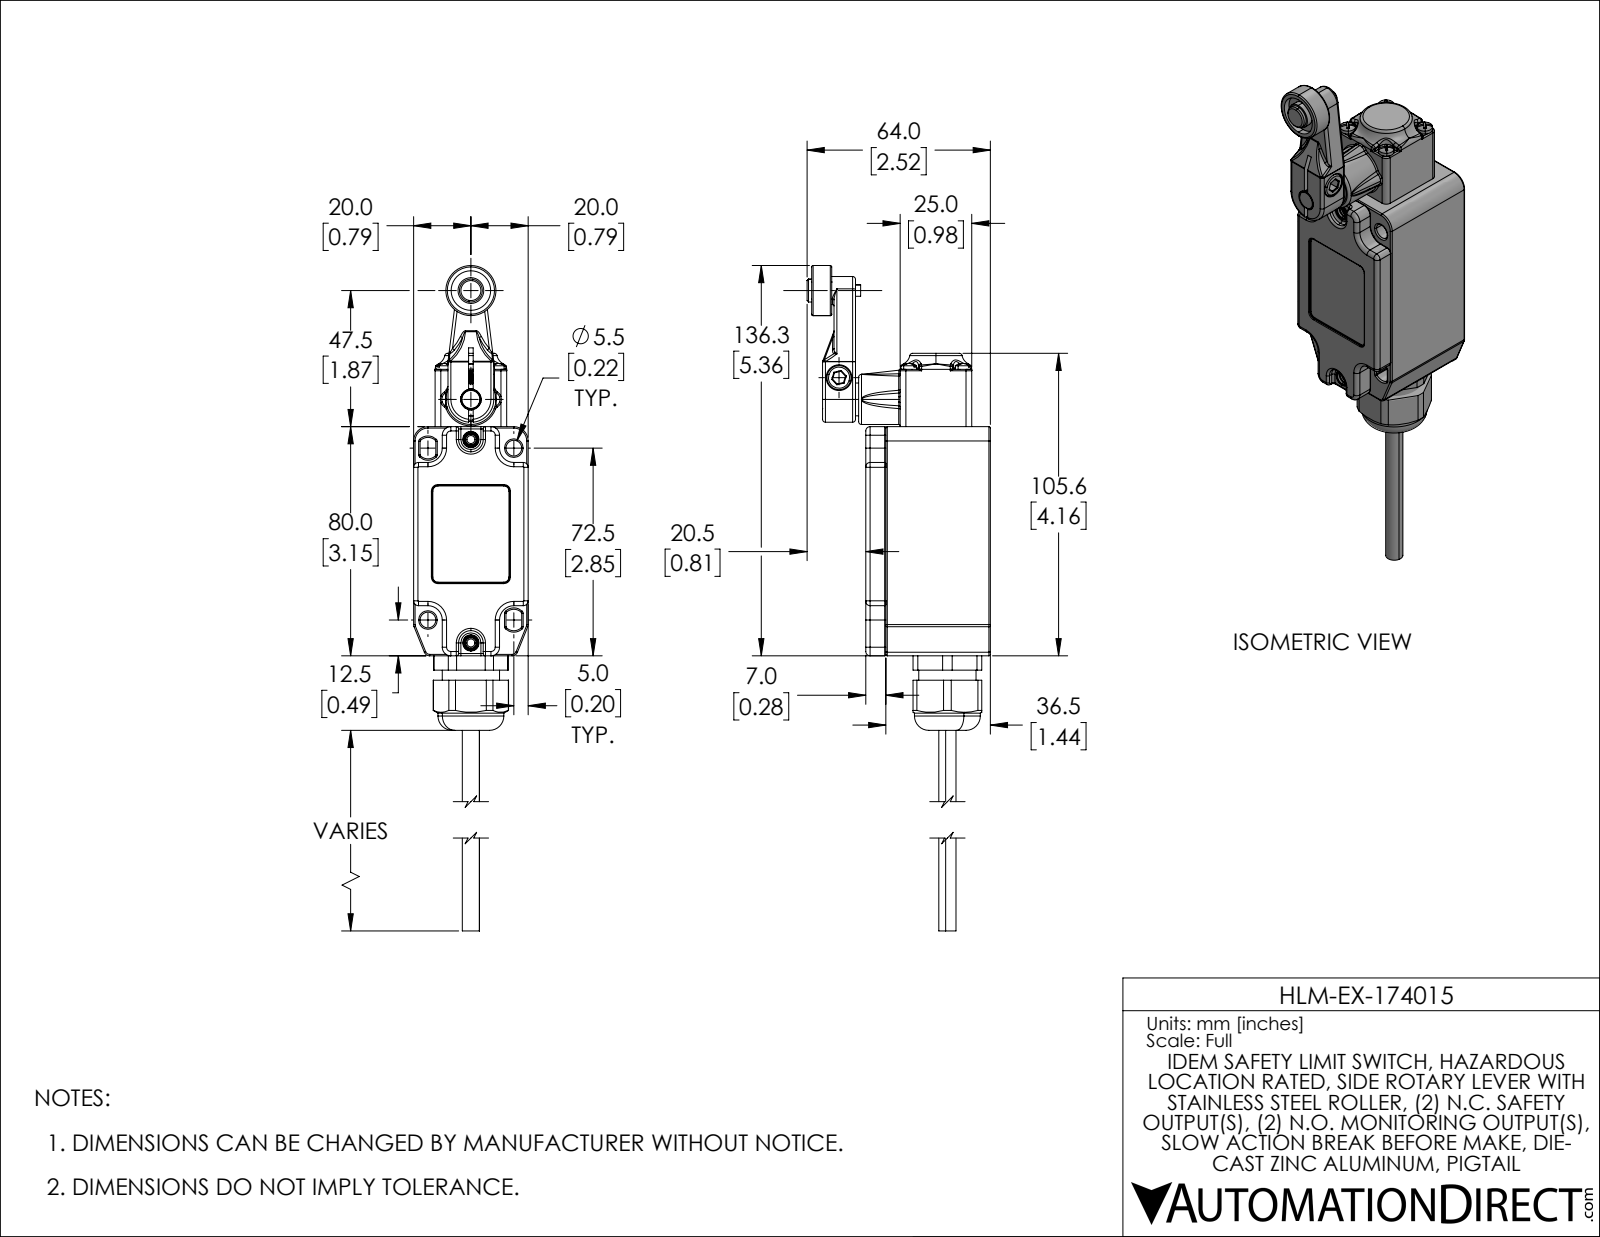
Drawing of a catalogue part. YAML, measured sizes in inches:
part_name: "HLM-EX-174015"
step_written_by: "SolidWorks 2021 (AUTOMOTIVE_DESIGN)"
units: inches
bodies: {solids: 15, faces: 2541, planar: 508, cylindrical: 609, other: 1424}
overall_size: [8.671, 2.52, 1.575]
volume: 5.931
surface_area: 90.96
round_holes:
  - {diameter: 0.118, count: 5}
  - {diameter: 0.106, count: 4}
  - {diameter: 0.134, count: 4}
  - {diameter: 0.146, count: 2}
  - {diameter: 0.15, count: 2}
  - {diameter: 0.157, count: 2}
  - {diameter: 0.165, count: 2}
  - {diameter: 0.217, count: 2}
  - {diameter: 0.354, count: 2}
  - {diameter: 0.571, count: 2}
  - {diameter: 0.138, count: 1}
  - {diameter: 0.161, count: 1}
round_bosses_or_shafts:
  - {diameter: 0.216, count: 4}
  - {diameter: 0.689, count: 2}
  - {diameter: 0.252, count: 2}
  - {diameter: 0.236, count: 2}
  - {diameter: 0.906, count: 1}
  - {diameter: 0.728, count: 1}
  - {diameter: 0.451, count: 1}
  - {diameter: 0.386, count: 1}
partial_cylinders:
  - {radius: 0.02, count: 161}
  - {radius: 0.039, count: 28}
  - {radius: 0.016, count: 26}
  - {radius: 0.006, count: 14}
  - {radius: 0.079, count: 12}
  - {radius: 0.031, count: 10}
  - {radius: 0.059, count: 9}
  - {radius: 0.197, count: 6}
face_to_face_distances: [0.089, 1.486, 1.575, 1.398, 0.415, 0.102, 0.276, 1.61, 1.195, 0.173]
hole_center_spacings: [0.529, 0.748, 0.432, 0.65, 1.058, 0.157, 0.335, 0.37]
